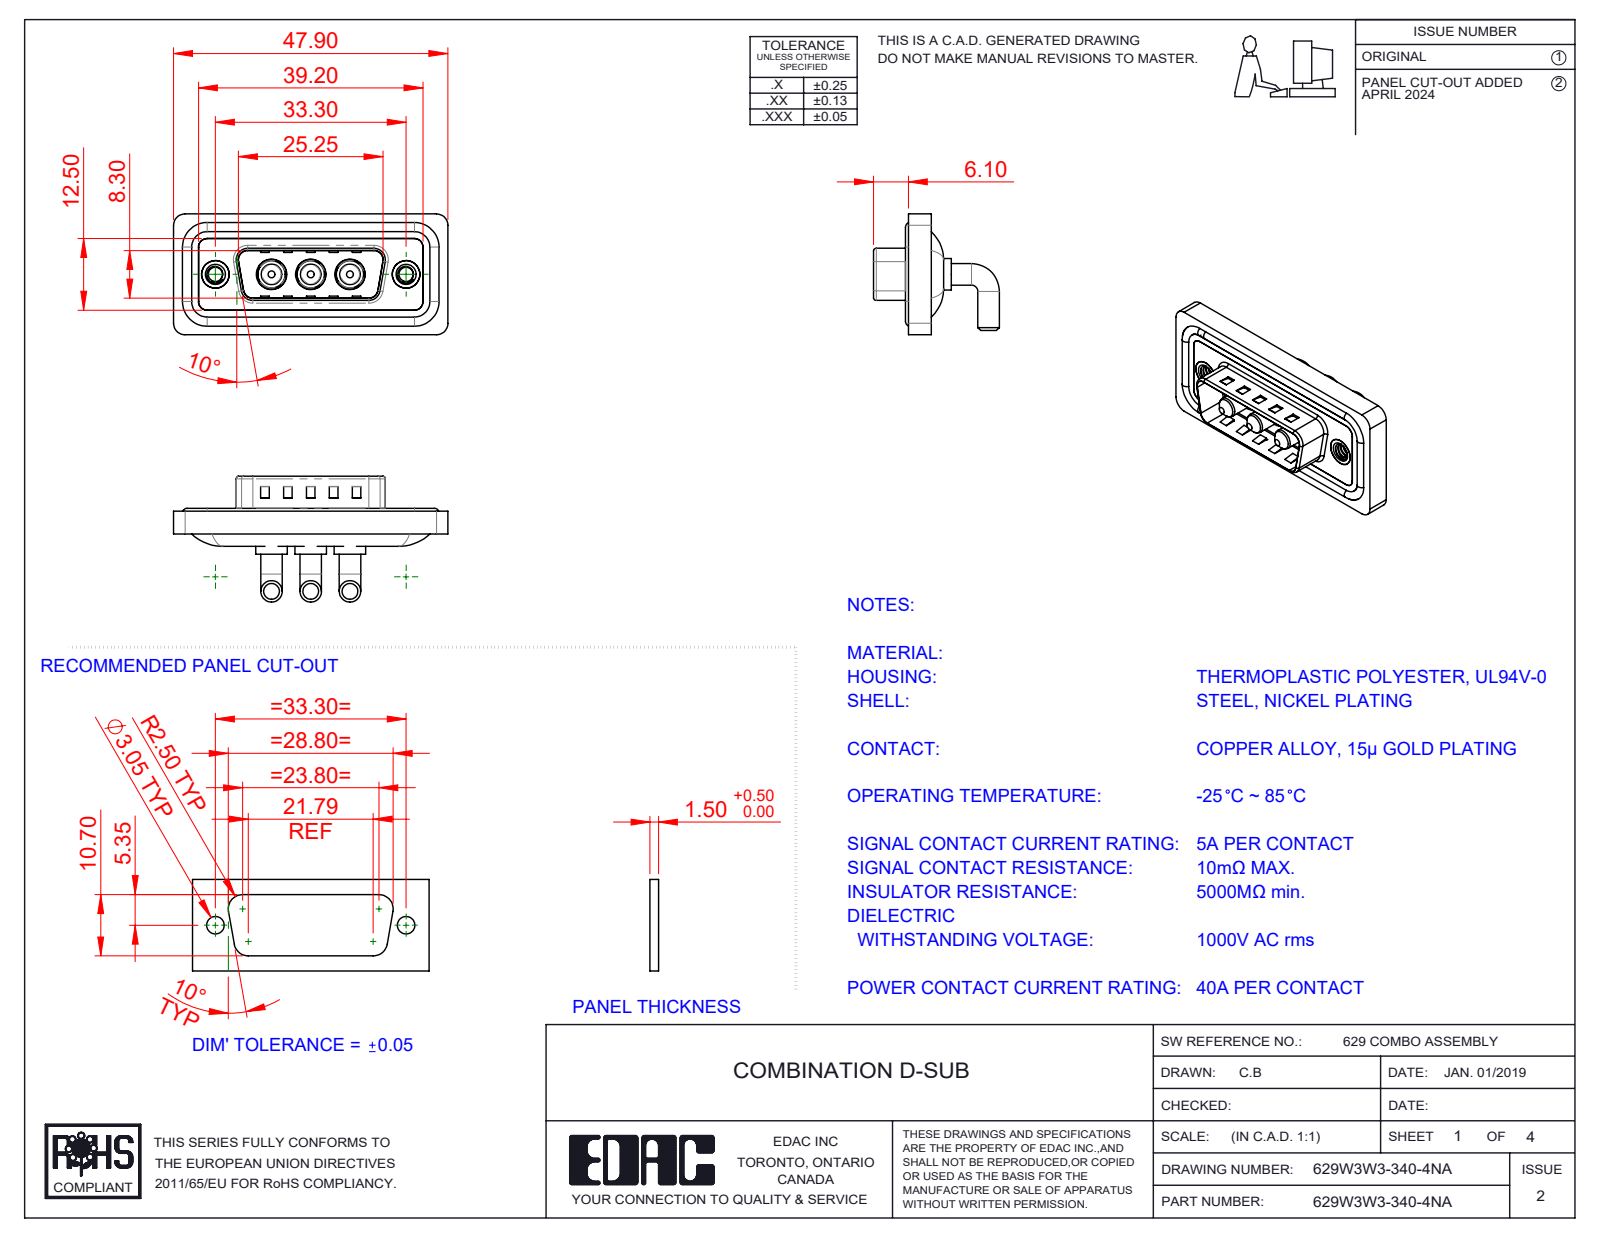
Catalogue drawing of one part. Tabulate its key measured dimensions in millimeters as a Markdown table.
| quantity | value |
| --- | --- |
| part name | 629W3W3-340-4NA; 629Combo Housing_3W3; 629Combo Waterproof Housing_15 Contacts; 629Combo Shell Rear_15 Contacts (+3 more) |
| STEP written by | SolidWorks 2023 (CONFIG_CONTROL_DESIGN) |
| units | millimeters |
| bodies | 13 solids, 570 faces (207 planar, 245 cylindrical, 118 other) |
| overall size | 47.9 × 21.98 × 21.1 |
| volume | 6 001 mm³ |
| surface area | 9 171 mm² |
| round holes (diameter × count) | 4.85 × 3, 5.3 × 3, 2.5 × 2, 4 × 2, 4.8 × 2, 5 × 2 |
| round bosses / shafts (diameter × count) | 3.75 × 6, 1.6 × 4, 5.5 × 3, 5.2 × 3, 4.75 × 3, 3.6 × 3, 4.9 × 2 |
| partial cylindrical surfaces (radius × count) | 2 × 20, 1.5 × 18, 0.5 × 8, 1.6 × 8, 0.25 × 4, 0.6 × 4, 0.65 × 4, 0.9 × 4 |
| main face-to-face distances | 0.4, 2.9, 0.8, 1.1, 2.1, 1.6, 3.1, 2.5, 4.5, 3.7 |
| hole center spacings | 6.85, 9.8, 16.65, 23.5, 13.7, 33.3 |
